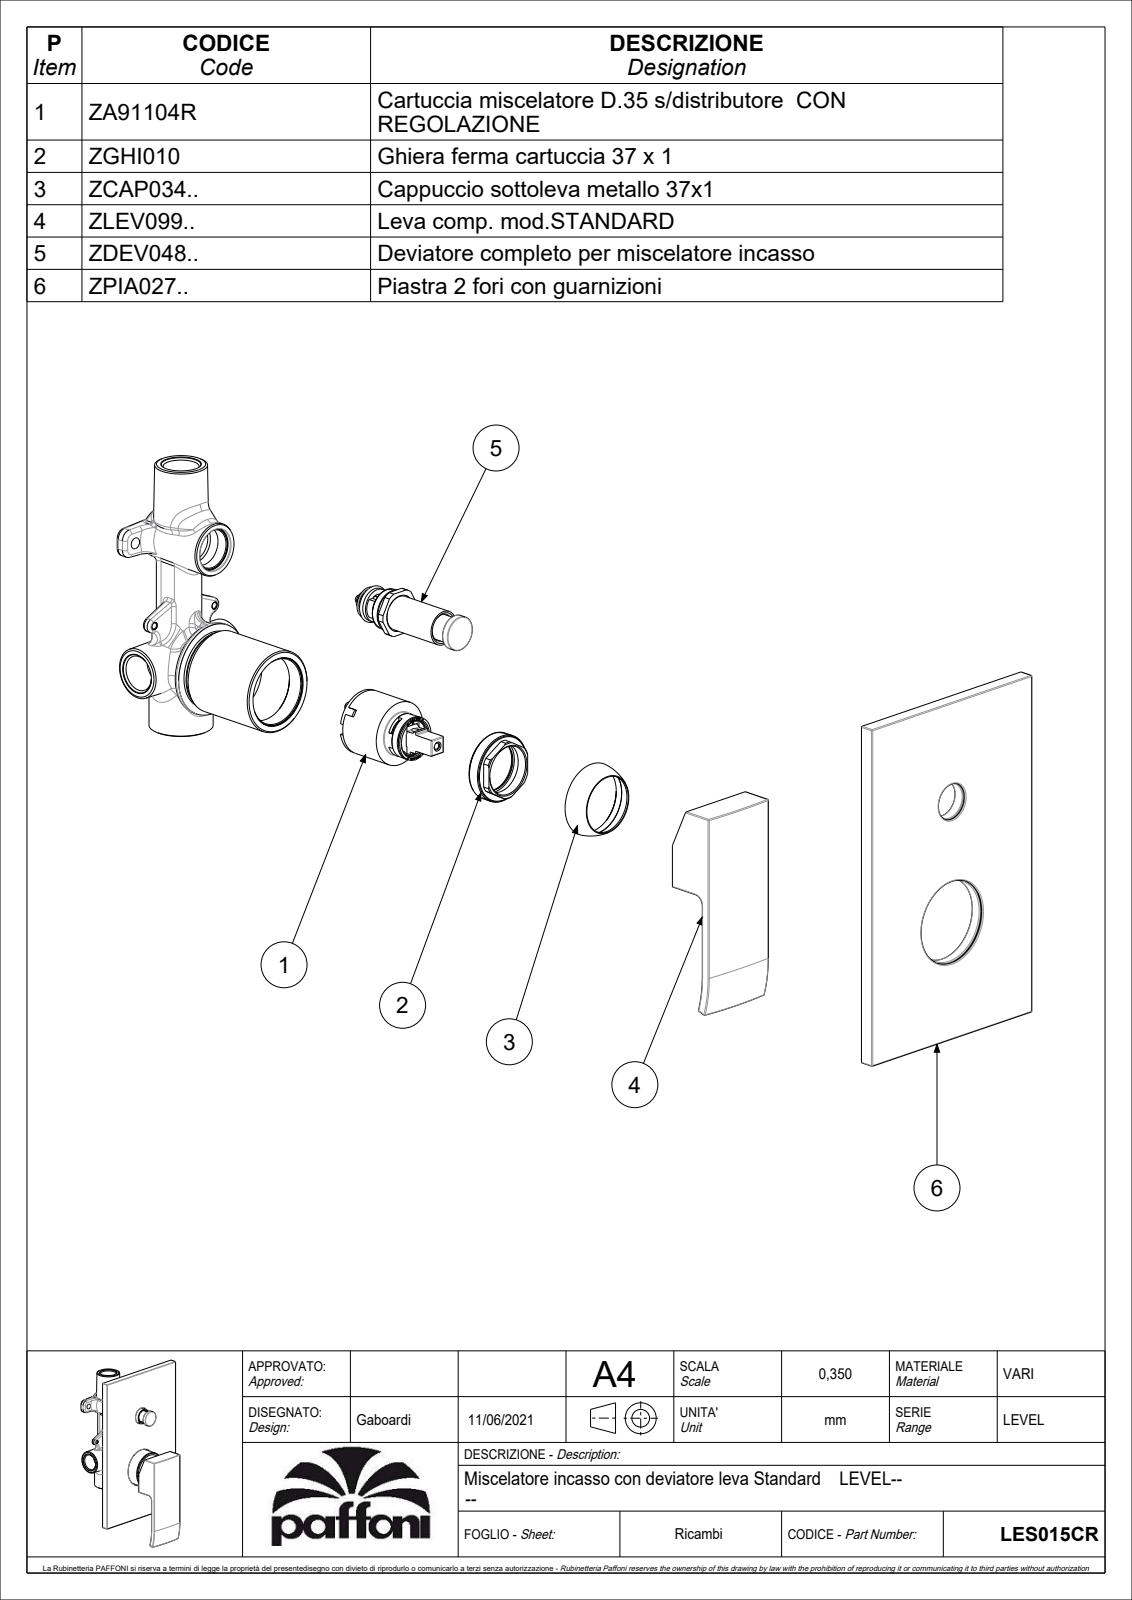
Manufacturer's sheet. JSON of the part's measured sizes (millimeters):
{"part_name": "LES015CR", "step_written_by": "CREO PARAMETRIC BY PTC INC, 2020044 (CONFIG_CONTROL_DESIGN)", "units": "millimeters", "bodies": {"solids": 5, "faces": 1048, "planar": 599, "cylindrical": 267, "other": 182}, "overall_size": [212.38, 120, 59.05], "volume_mm3": 181589, "surface_area_mm2": 123043, "round_holes": [[4, 2], [3, 1], [3.3, 1], [5, 1], [5.5, 1], [7.8, 1], [10.5, 1], [14.8, 1], [19.2, 1], [19.5, 1], [19.9, 1], [20, 1]], "round_bosses_or_shafts": [[51, 1], [49, 1], [44.8, 1], [35, 1], [32.2, 1], [25, 1], [23.5, 1], [23.4, 1]], "partial_cylinders_radius": [[0.5, 41], [1.5, 14], [0.15, 11], [1, 10], [0.3, 4], [2, 4], [300, 2], [2.25, 1]], "face_to_face_distances": [2.5, 5.5, 8, 0.5, 3, 5, 37.5, 82.5, 22.5, 45], "hole_center_spacings": [8, 68]}
